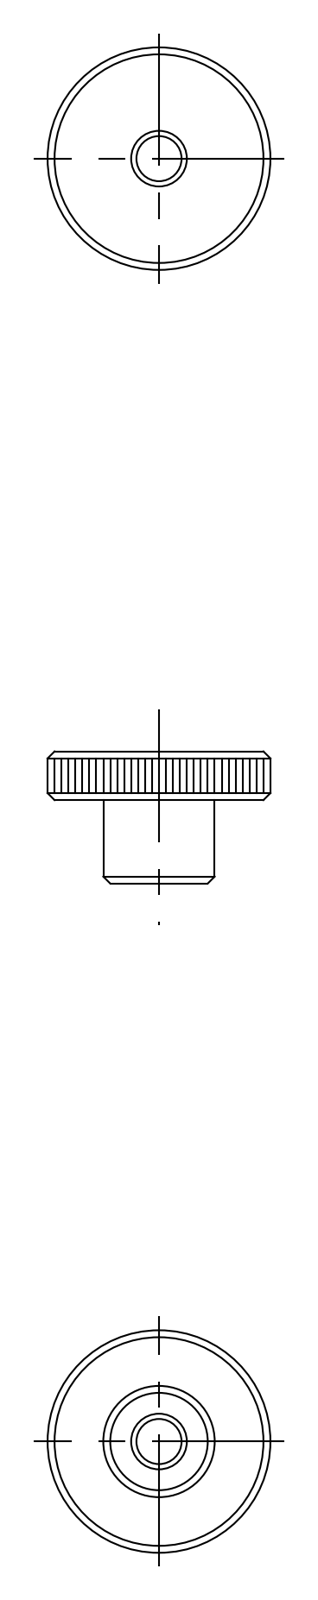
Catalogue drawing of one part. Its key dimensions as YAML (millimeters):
part_name: "knob"
step_written_by: "CADfix (AUTOMOTIVE_DESIGN)"
units: millimeters
bodies: {solids: 1, faces: 15, planar: 0, cylindrical: 0, other: 15}
overall_size: [16, 16, 9.5]
volume: 872
surface_area: 786
